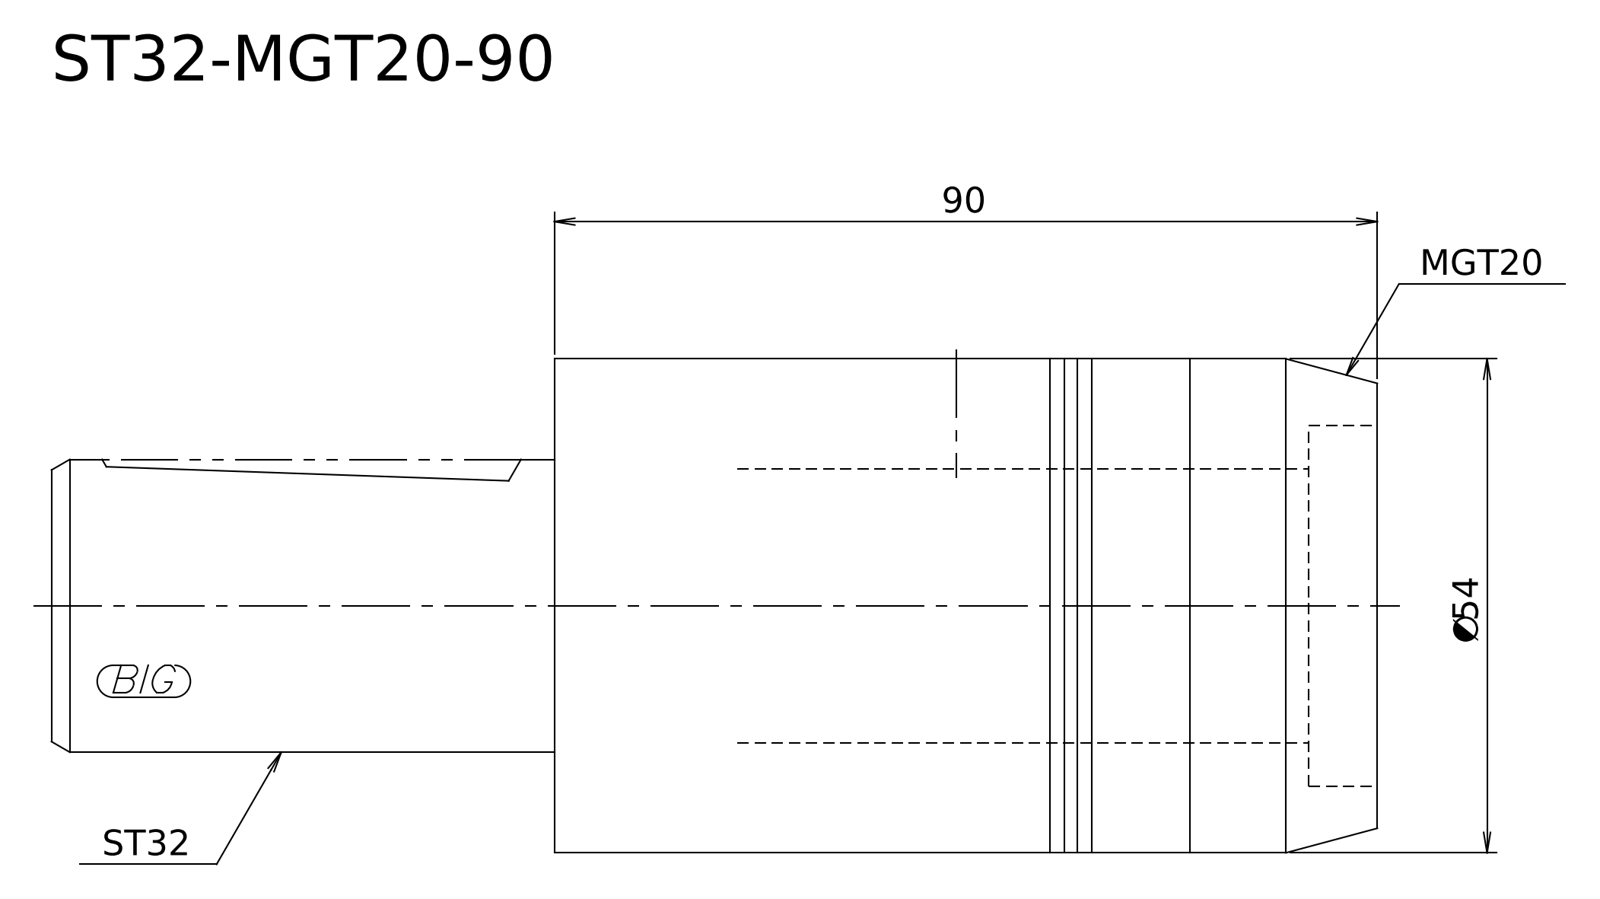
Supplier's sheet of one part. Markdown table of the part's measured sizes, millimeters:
| quantity | value |
| --- | --- |
| STEP written by | Kubotek KeyCreator V8.5.1 (14335) (CONFIG_CONTROL_DESIGN) |
| units | millimeters |
| bodies | 1 solid, 6 faces (3 planar, 2 cylindrical, 1 other) |
| overall size | 145 × 54 × 54 |
| volume | 248 156 mm³ |
| surface area | 24 918 mm² |
| round bosses / shafts (diameter × count) | 54 × 1, 32 × 1 |
| main face-to-face distances | 90, 145, 55 |
